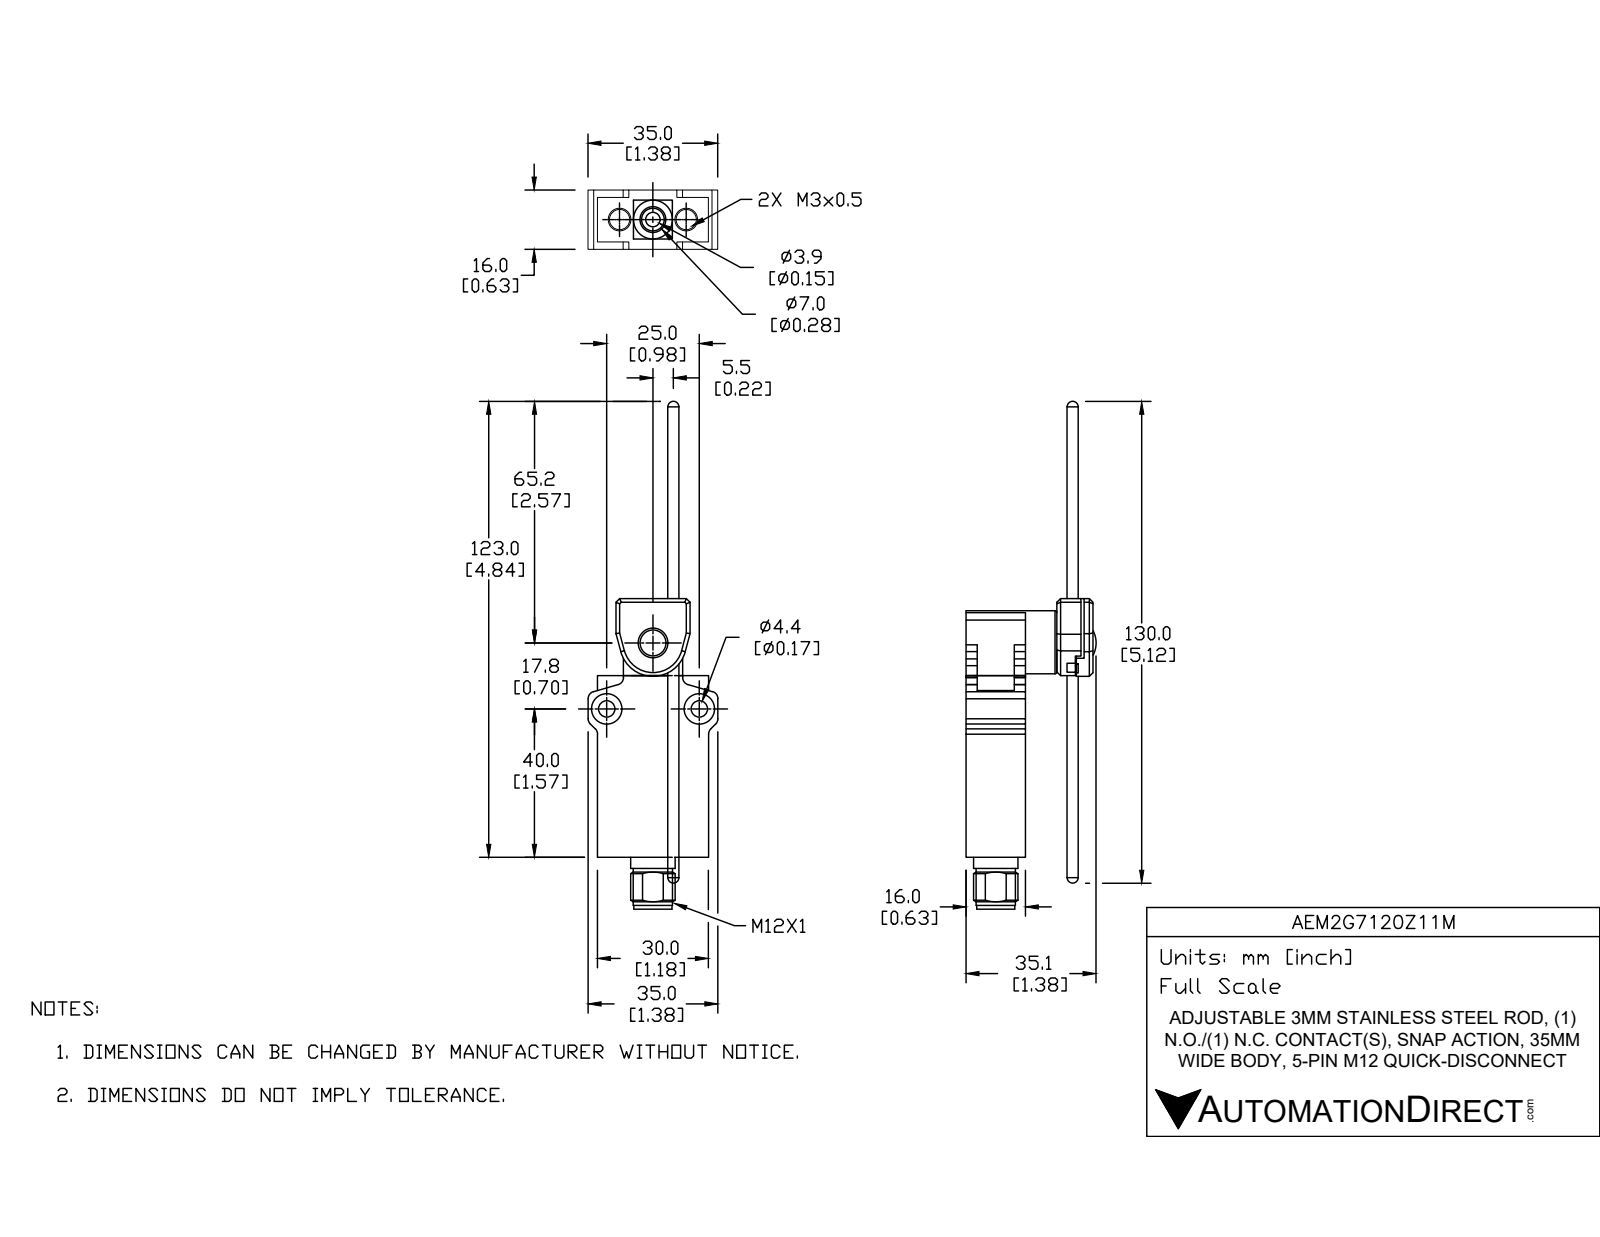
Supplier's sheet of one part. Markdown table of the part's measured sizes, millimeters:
| quantity | value |
| --- | --- |
| part name | AEM2G7120Z11M |
| STEP written by | SolidWorks 2017 (AUTOMOTIVE_DESIGN) |
| units | millimeters |
| bodies | 6 solids, 272 faces (142 planar, 85 cylindrical, 45 other) |
| overall size | 181.4 × 35 × 34.7 |
| volume | 33 950 mm³ |
| surface area | 13 570 mm² |
| round holes (diameter × count) | 3 × 2, 4.4 × 2, 8.2 × 2, 3.5 × 1, 5 × 1, 8 × 1 |
| round bosses / shafts (diameter × count) | 15.8 × 1, 12 × 1, 10.6 × 1, 10.3 × 1, 7 × 1, 3 × 1 |
| partial cylindrical surfaces (radius × count) | 2 × 8, 1.5 × 1, 4.4 × 1, 6.5 × 1, 6.6 × 1, 9 × 1 |
| main face-to-face distances | 16, 30, 4.3, 12, 7.1, 22.9, 2.5, 17.7, 25.1, 52 |
| hole center spacings | 22, 19, 25 |
